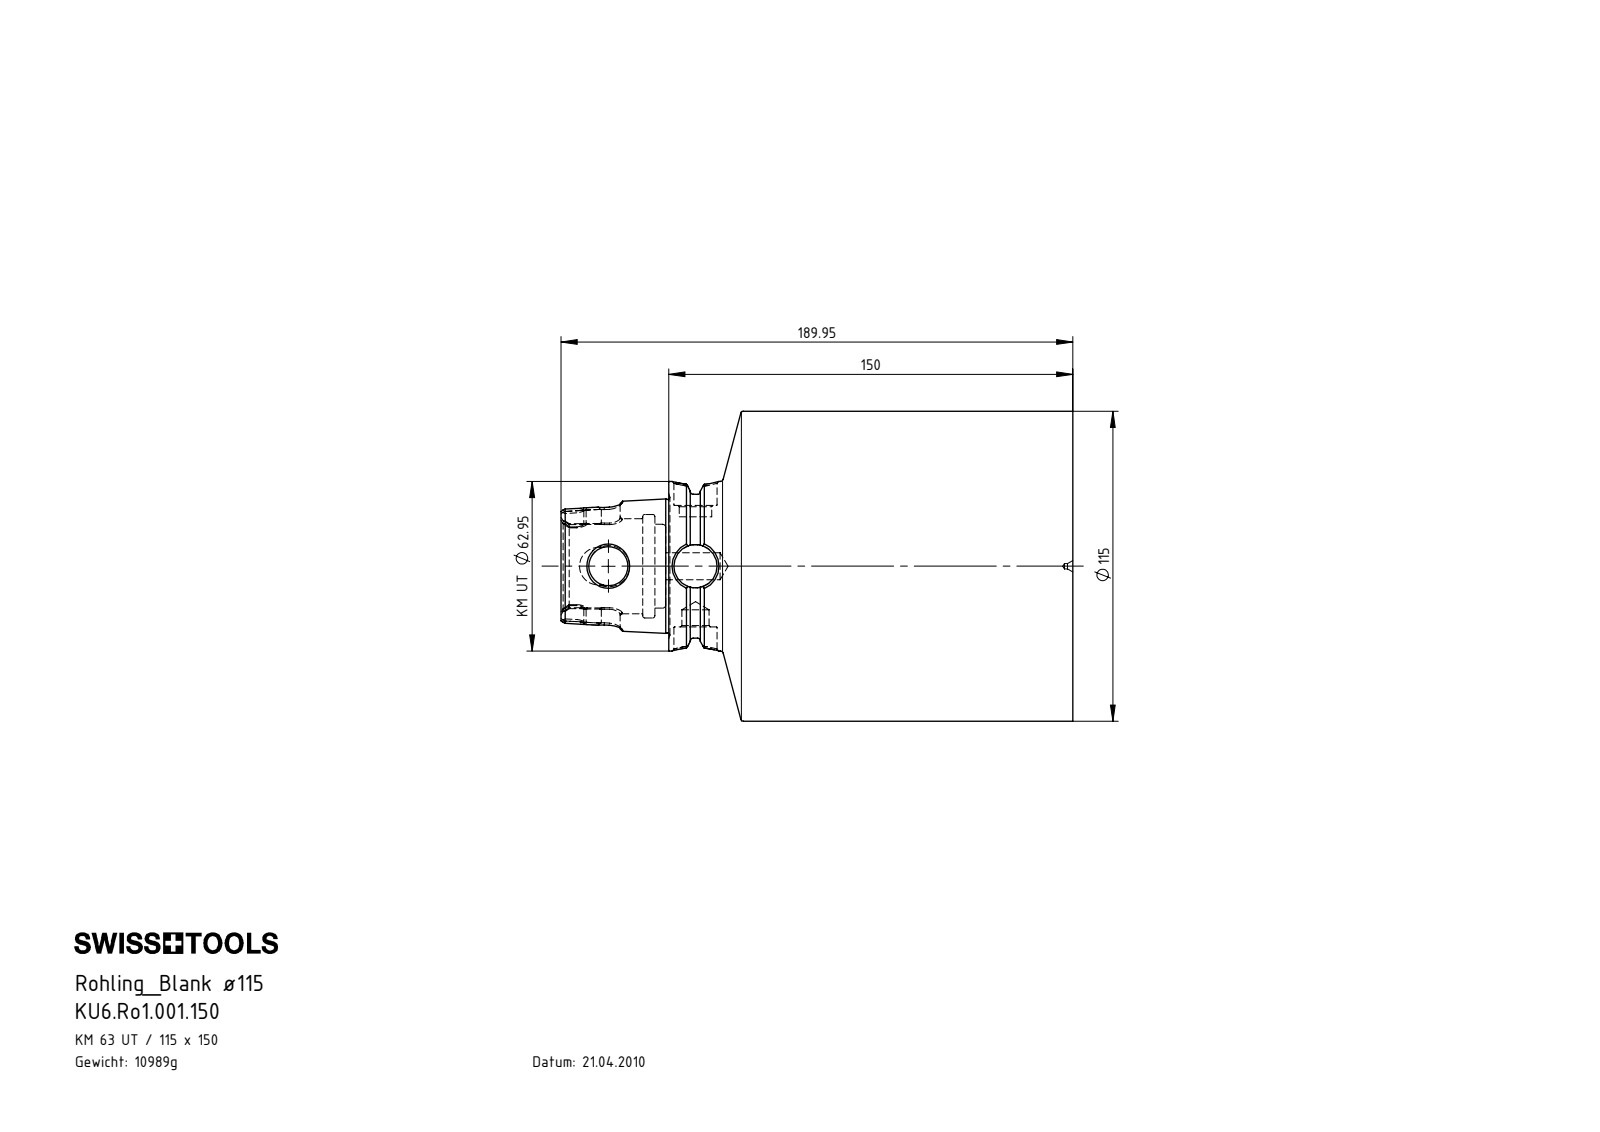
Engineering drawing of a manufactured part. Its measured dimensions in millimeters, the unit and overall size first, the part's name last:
Units: millimetres
Overall size (bounding box): 189.95 × 115 × 115
Round holes (diameter × count): ⌀16.05 ×2, ⌀2 ×1, ⌀10 ×1, ⌀10.1 ×1, ⌀12.1 ×1, ⌀14.5 ×1, ⌀31.1 ×1, ⌀35.27 ×1, ⌀38.4 ×1
Round bosses / shafts (diameter × count): ⌀115 ×1, ⌀62.95 ×1
Partial cylindrical surfaces — rounded edges, fillets, slot ends (radius × count): R4 ×6, R7.04 ×2, R27.85 ×1
Main face-to-face distances: 150, 1.1, 151.1, 4.05, 5.15, 155.15, 45.1, 34.8, 38.85, 39.95
Hole centre spacings: 32.35
Volume: 1 385 000 mm³ · Surface area: 80 696 mm²
Bodies: 1 solid, 234 faces (50 planar, 52 cylindrical, 132 other)
Part name (STEP PRODUCT): KU6.Ro1.001.150
STEP written by: SolidWorks 2017 (CONFIG_CONTROL_DESIGN)
